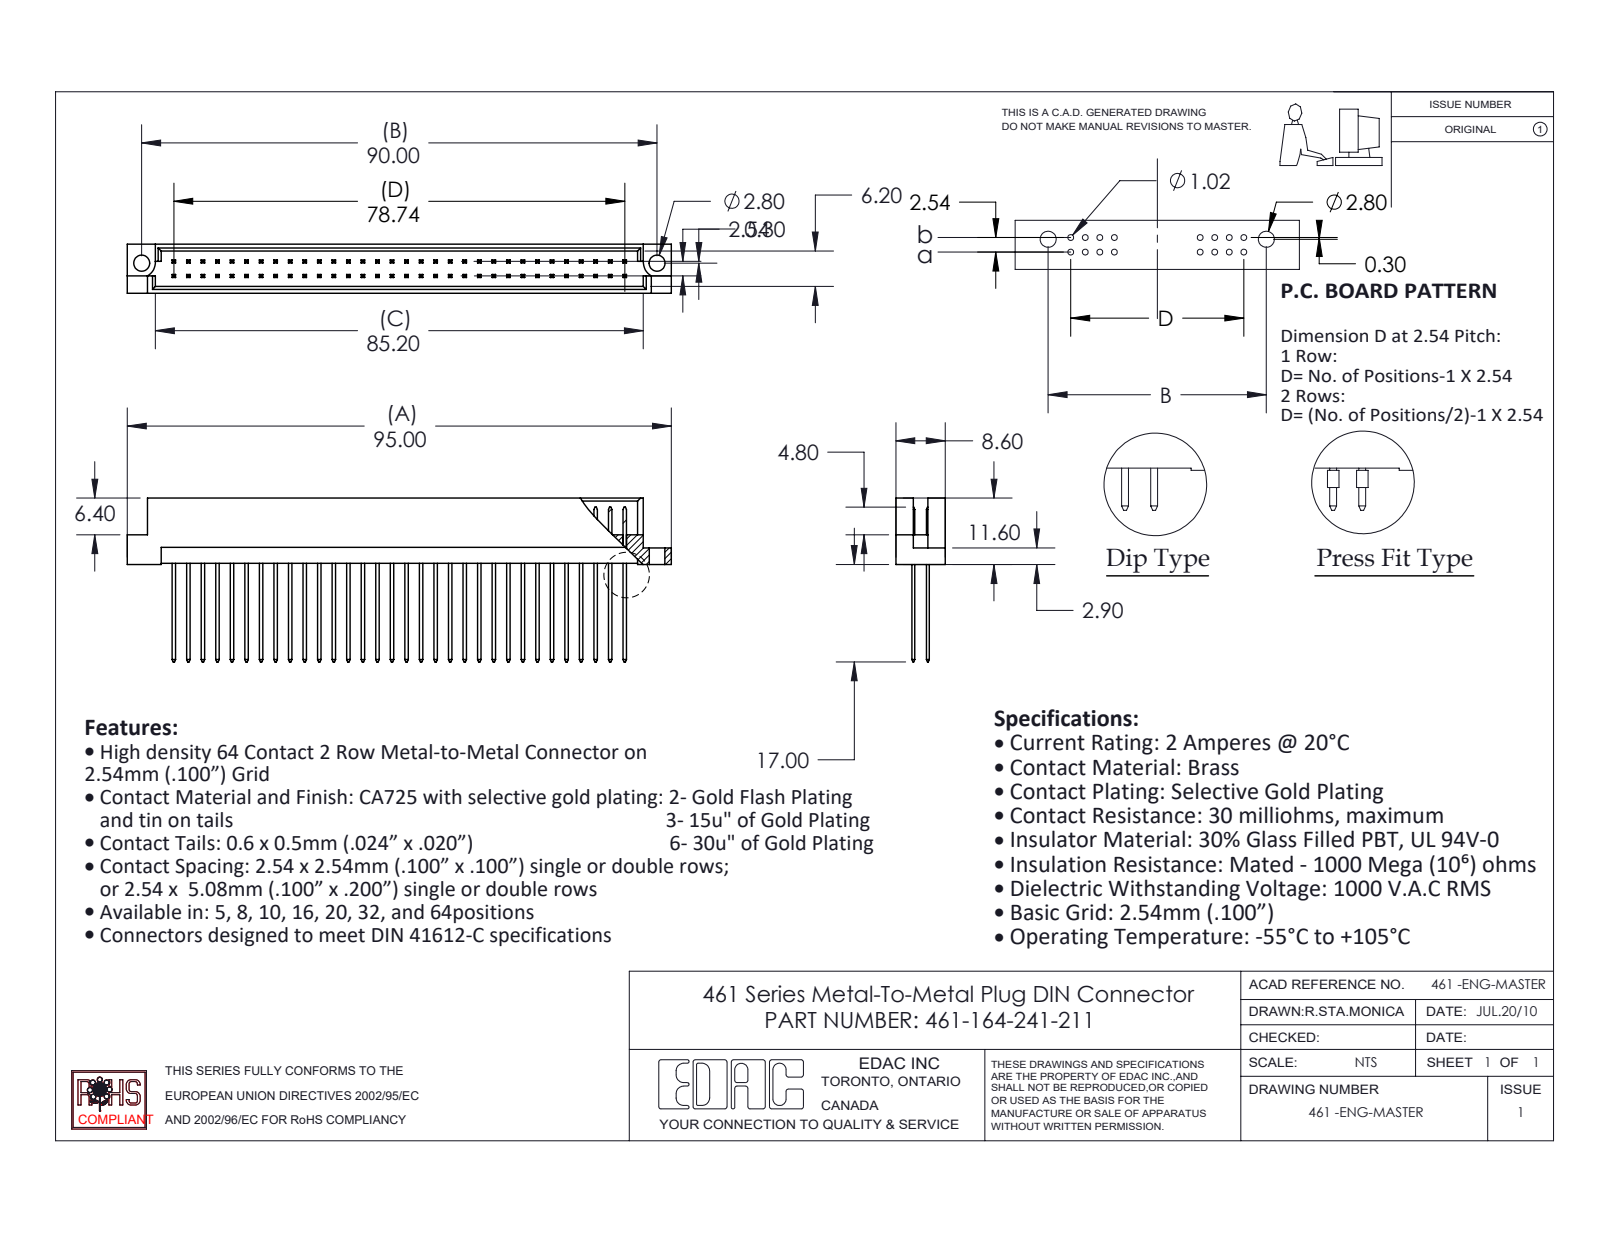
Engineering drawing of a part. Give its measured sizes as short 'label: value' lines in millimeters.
name: 461-290_41; 461 Part_64; 461-164-241-211
written by: SolidWorks 2020 (CONFIG_CONTROL_DESIGN)
unit: mm
bodies: 65 solids, 1201 faces (1194 planar, 7 cylindrical, 0 other)
size: 95 × 28.6 × 8.6
volume: 5 167 mm³; area: 9 448 mm²
holes: 2× ⌀2.8
rounds: 2× R2.8
face distances: 2.54, 1.2, 7.4, 2.78, 3.28, 5.32, 5.82, 1.58, 2.08, 4.12
hole spacings: 90
